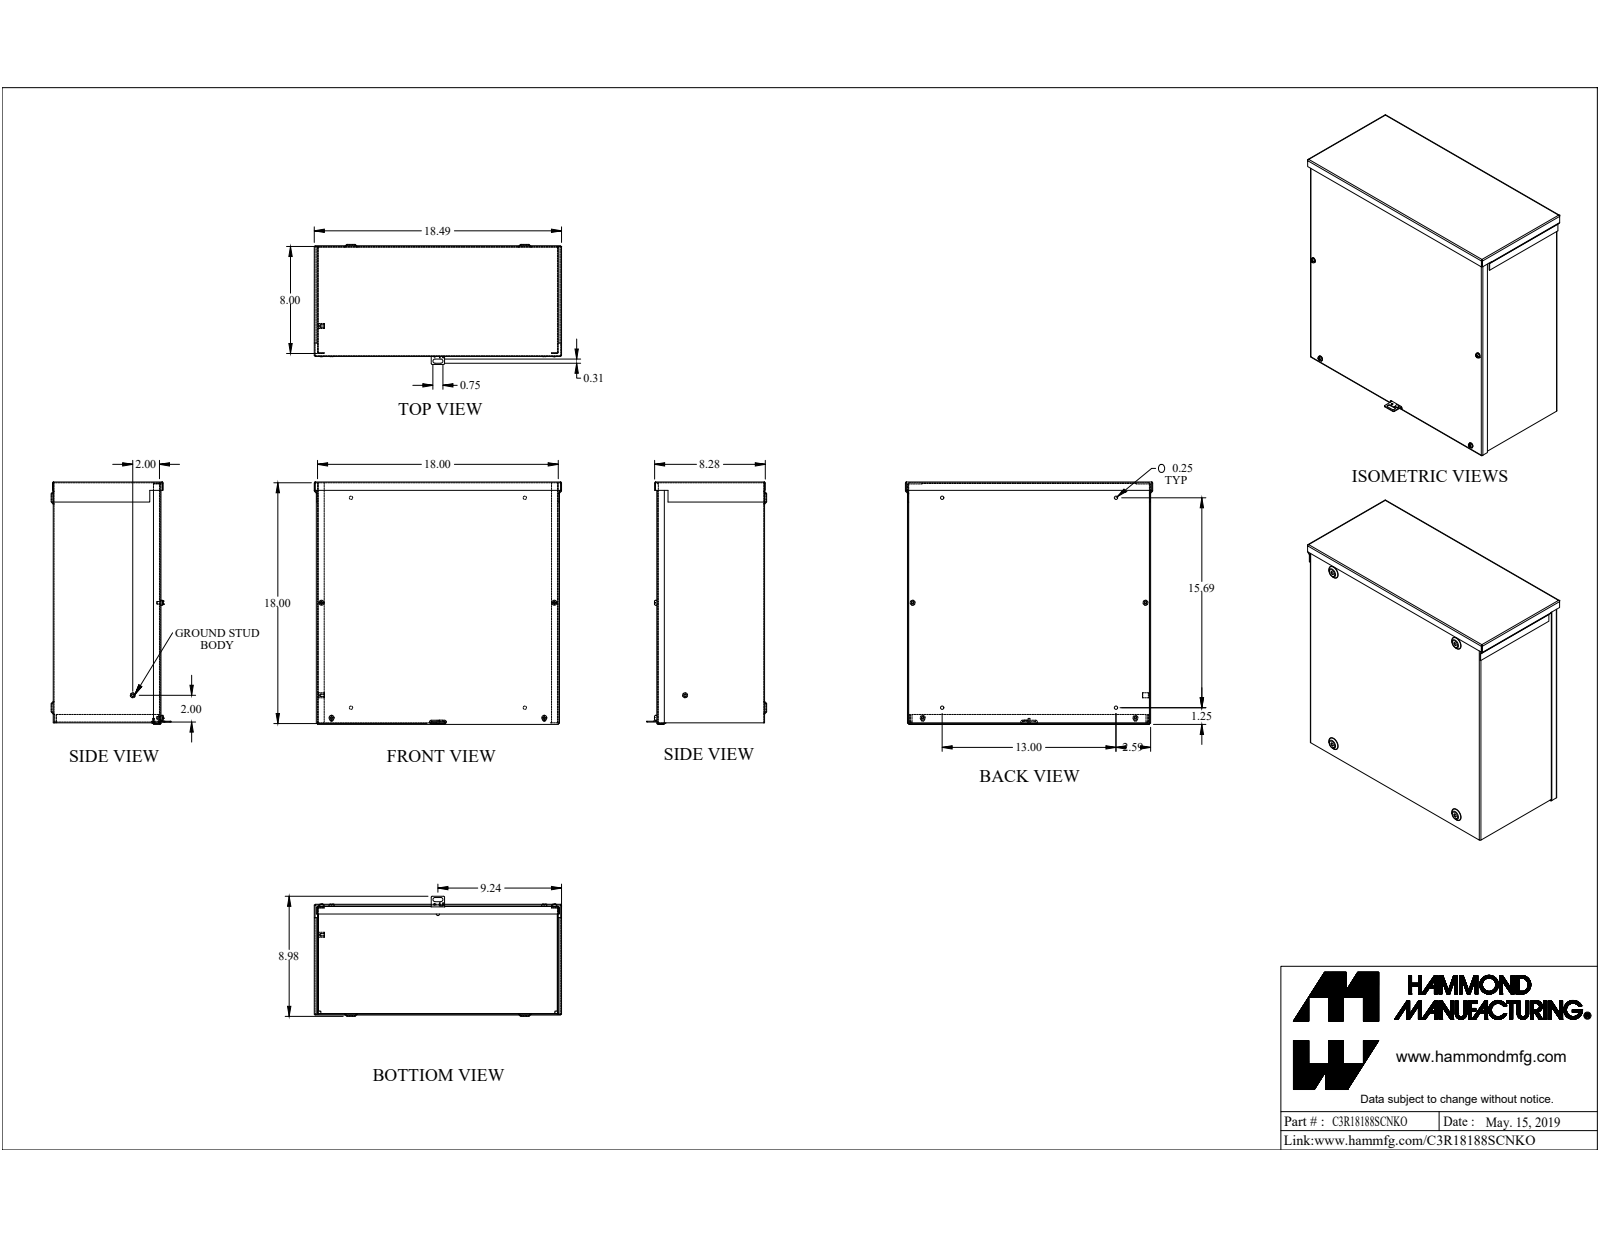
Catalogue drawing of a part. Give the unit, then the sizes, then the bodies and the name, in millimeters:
Units: millimetres
Overall size (bounding box): 469.6 × 460.2 × 228
Round holes (diameter × count): ⌀4.3 ×4, ⌀6.4 ×4, ⌀3.2 ×1, ⌀3.5 ×1, ⌀4 ×1
Round bosses / shafts (diameter × count): ⌀4.8 ×4, ⌀9.5 ×3, ⌀9.5 ×2, ⌀3.2 ×1
Partial cylindrical surfaces — rounded edges, fillets, slot ends (radius × count): R0.7 ×21, R2.2 ×21, R2.8 ×8, R3.2 ×8, R4 ×2
Main face-to-face distances: 1.4, 203.2, 455.8, 201.8, 204.6, 457.2, 1.4, 454.3, 454.3, 455.8
Hole centre spacings: 207, 434.6, 42.9, 221.2, 330.2, 368.1, 398.6, 421.4
Volume: 1 280 000 mm³ · Surface area: 1 751 000 mm²
Bodies: 11 solids, 339 faces (211 planar, 84 cylindrical, 44 other)
Part name (STEP PRODUCT): C3R18188SCNKO
STEP written by: SolidWorks 2019 (AUTOMOTIVE_DESIGN)
